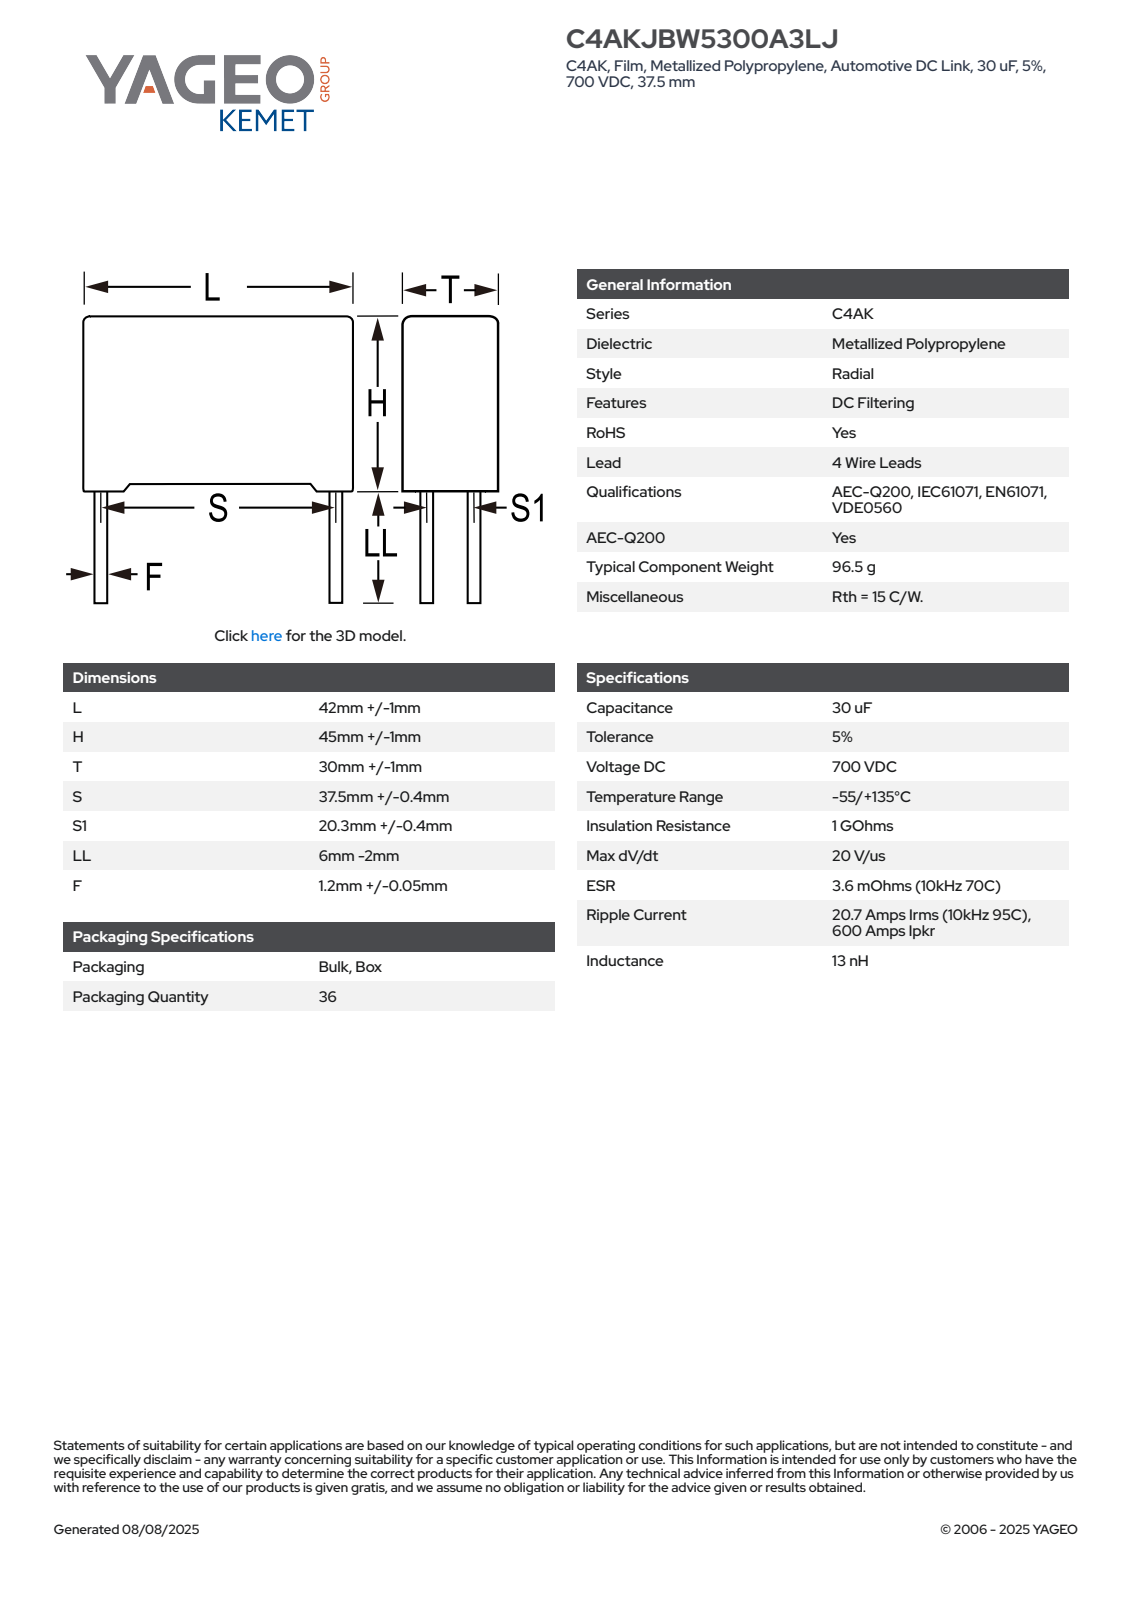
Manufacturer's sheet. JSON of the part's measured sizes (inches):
{"part_name": "CFP_RB4_42X45X30_L43H46T31S37.5S120.3LL4F1.25", "step_written_by": "SolidWorks 2014 (AUTOMOTIVE_DESIGN)", "units": "inches", "bodies": {"solids": 4, "faces": 87, "planar": 79, "cylindrical": 8, "other": 0}, "overall_size": [1.969, 1.693, 1.22], "volume_in3": 3.647, "surface_area_in2": 15.05, "round_bosses_or_shafts": [[0.049, 4]], "face_to_face_distances": [1.22, 1.693, 1.758, 0.053, 1.811, 0.075, 1.618, 1.221, 1.543, 1.145]}
